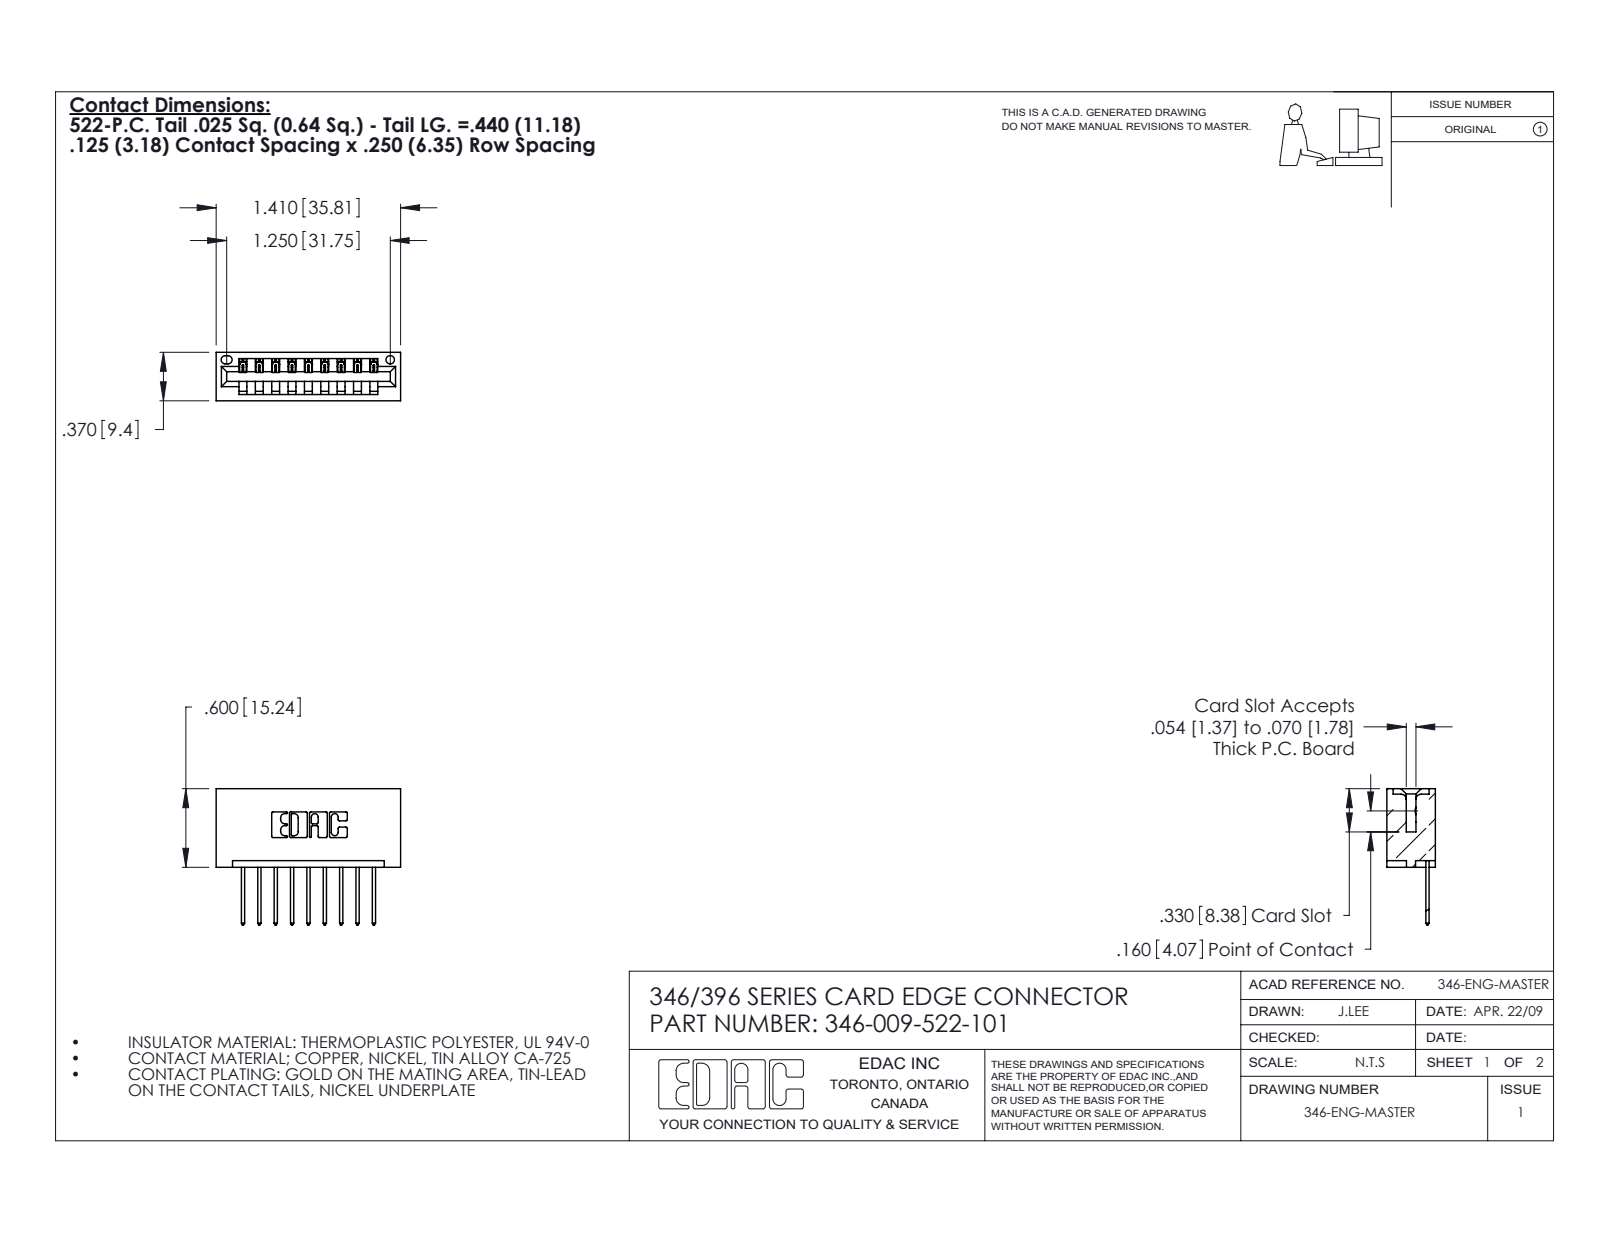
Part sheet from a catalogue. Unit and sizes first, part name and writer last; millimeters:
Units: millimetres
Overall size (bounding box): 35.8 × 26.4 × 9.4
Round holes (diameter × count): ⌀1.6 ×1
Partial cylindrical surfaces — rounded edges, fillets, slot ends (radius × count): R0.3 ×22, R0.2 ×18, R0.3 ×18, R0.2 ×6, R0.8 ×6, R0.7 ×3, R0.8 ×2, R1 ×2
Main face-to-face distances: 6.4, 1.2, 8.2, 9.4, 12.7, 1.8, 7.6, 0.6, 3.2, 4.7
Volume: 3 750 mm³ · Surface area: 4 441 mm²
Bodies: 10 solids, 636 faces (432 planar, 204 cylindrical, 0 other)
Part name (STEP PRODUCT): 346 Part_No Mounting Lugs; 345-292-001_345-293-122; 346-009-522-101
STEP written by: SolidWorks 2020 (CONFIG_CONTROL_DESIGN)
